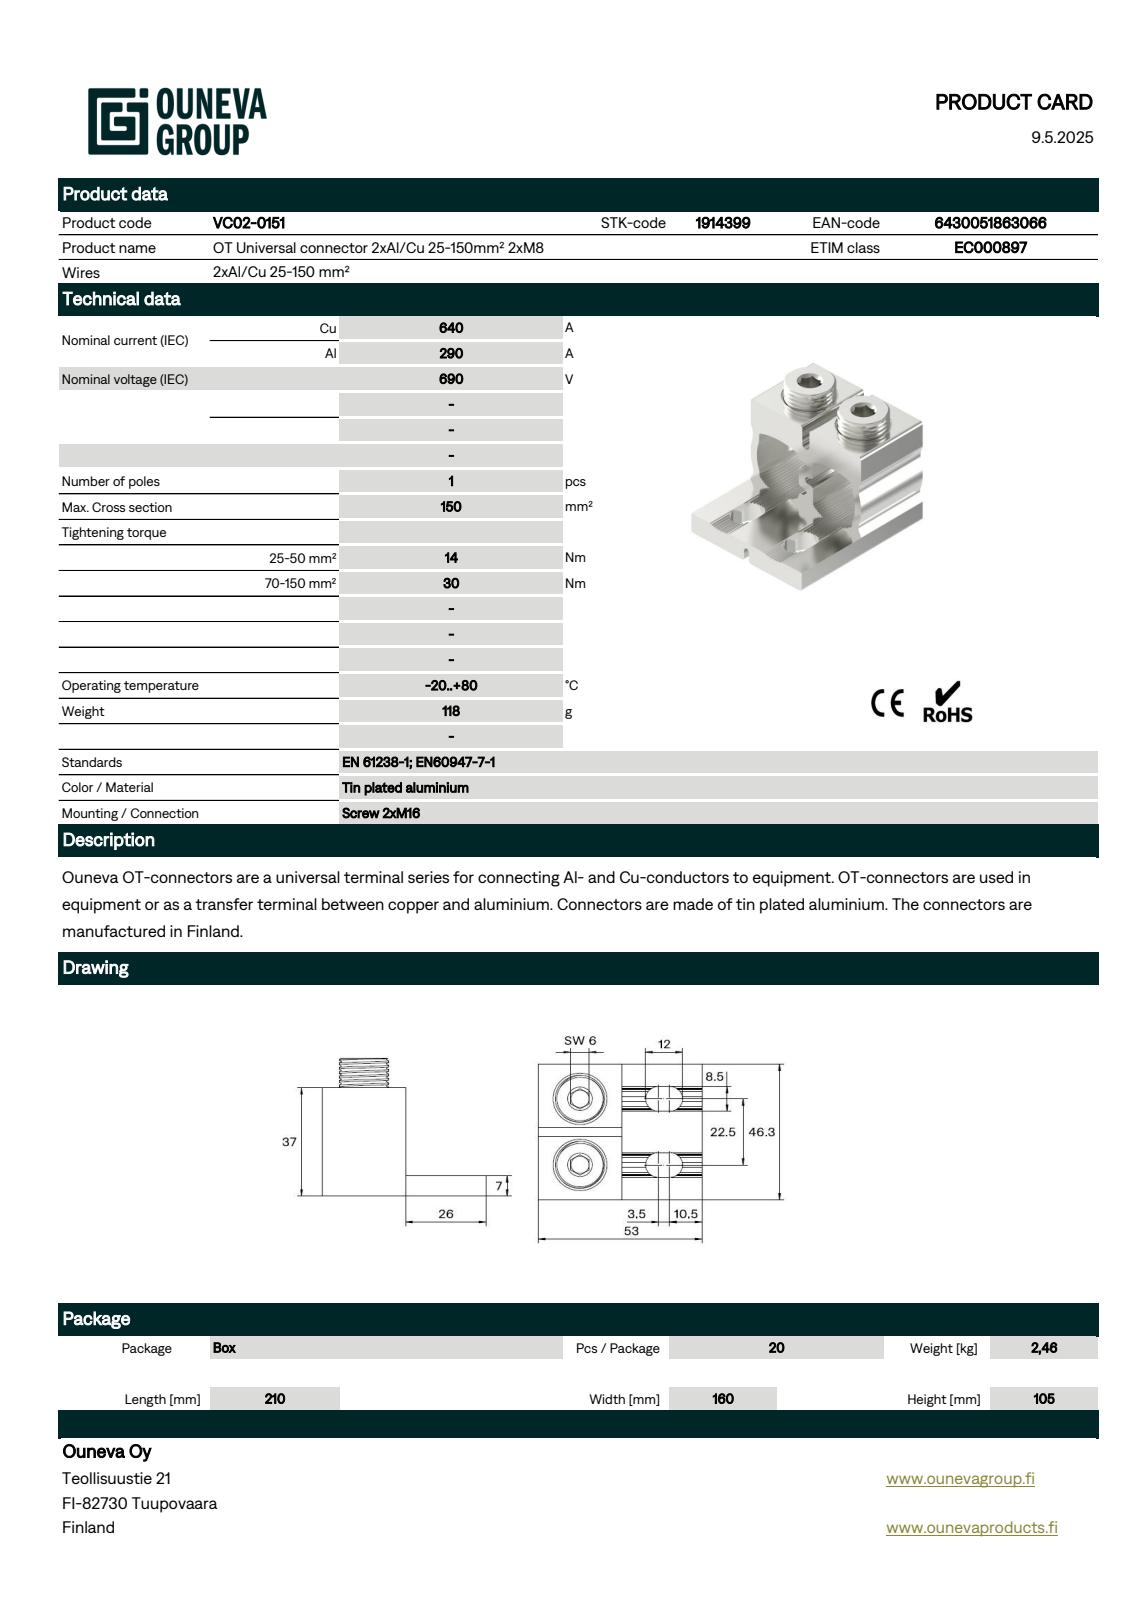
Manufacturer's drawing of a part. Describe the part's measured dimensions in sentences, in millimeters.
The part is named "VC02-0151_OT_2x150_2xM8". Its 3-D file was written by "Creo Elements/Direct Modeling 20.6A 14-Oct-2023 (C) Parametric Technology GmbH (AUTOMOTIVE_DESIGN)". It is 1 solid with 253 faces: 68 planar, 173 cylindrical and 12 other. Overall it measures 53 by 49 by 46.3 millimeters. Its volume is 37 520 cubic millimeters and its surface area 16 347 square millimeters. Round bosses or shafts: 2 of diameter 16. Partial cylindrical surfaces (rounded edges, fillets, slot ends): 62 of radius 0.25, 20 of radius 0.15, 15 of radius 1, 7 of radius 1.25, 4 of radius 2.25, 4 of radius 4.25, 2 of radius 3.4, 2 of radius 6. The main face-to-face distances are 7, 37, 30, 27, 46.3, 2.5, 26, 22.15, 24.15, 2.
